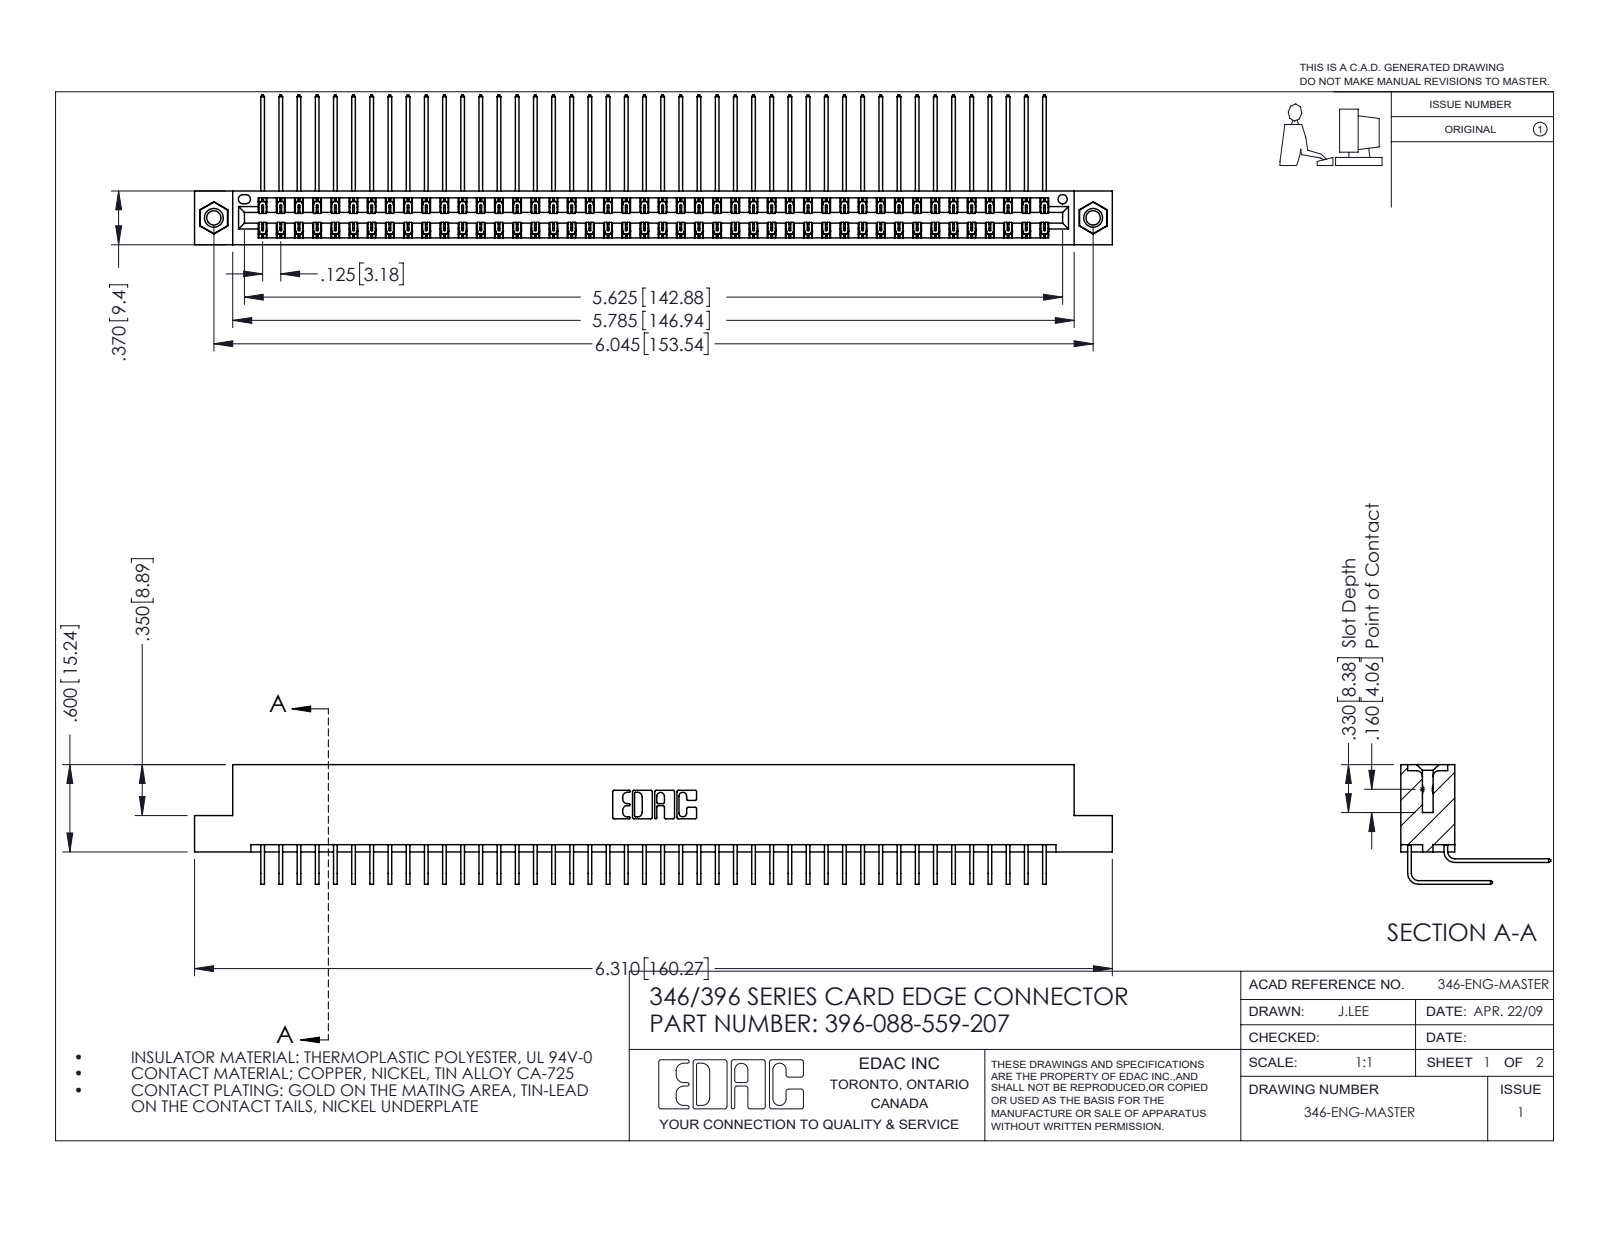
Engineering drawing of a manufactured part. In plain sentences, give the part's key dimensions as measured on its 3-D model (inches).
The part is named "345-292-001_558 559 Tail - 1; 345-292-001_559 Tail - 2; 396-088-559-207; 346 Part_Flush Mounting Lugs - 0.156 Dia-TI (+1 more)". Its 3-D file was written by "SolidWorks 2016 (CONFIG_CONTROL_DESIGN)". It is 91 solids with 4934 faces: 3364 planar, 1554 cylindrical and 16 other. Overall it measures 6.31 by 1.03 by 0.823 inches. Its volume is 0.985 cubic inches and its surface area 38.26 square inches. Round holes: 2 of diameter 0.098, 2 of diameter 0.125, 2 of diameter 0.156, 1 of diameter 0.064. Round bosses or shafts: 2 of diameter 0.155. Partial cylindrical surfaces (rounded edges, fillets, slot ends): 132 of radius 0.006, 22 of radius 0.01, 6 of radius 0.007, 6 of radius 0.031, 3 of radius 0.026, 2 of radius 0.014, 2 of radius 0.022, 2 of radius 0.024. The main face-to-face distances are 0.048, 0.322, 0.025, 0.37, 0.25, 0.072, 0.298, 0.275, 0.148, 0.222. The hole center spacings are 0.246, 5.836, 6.045.
